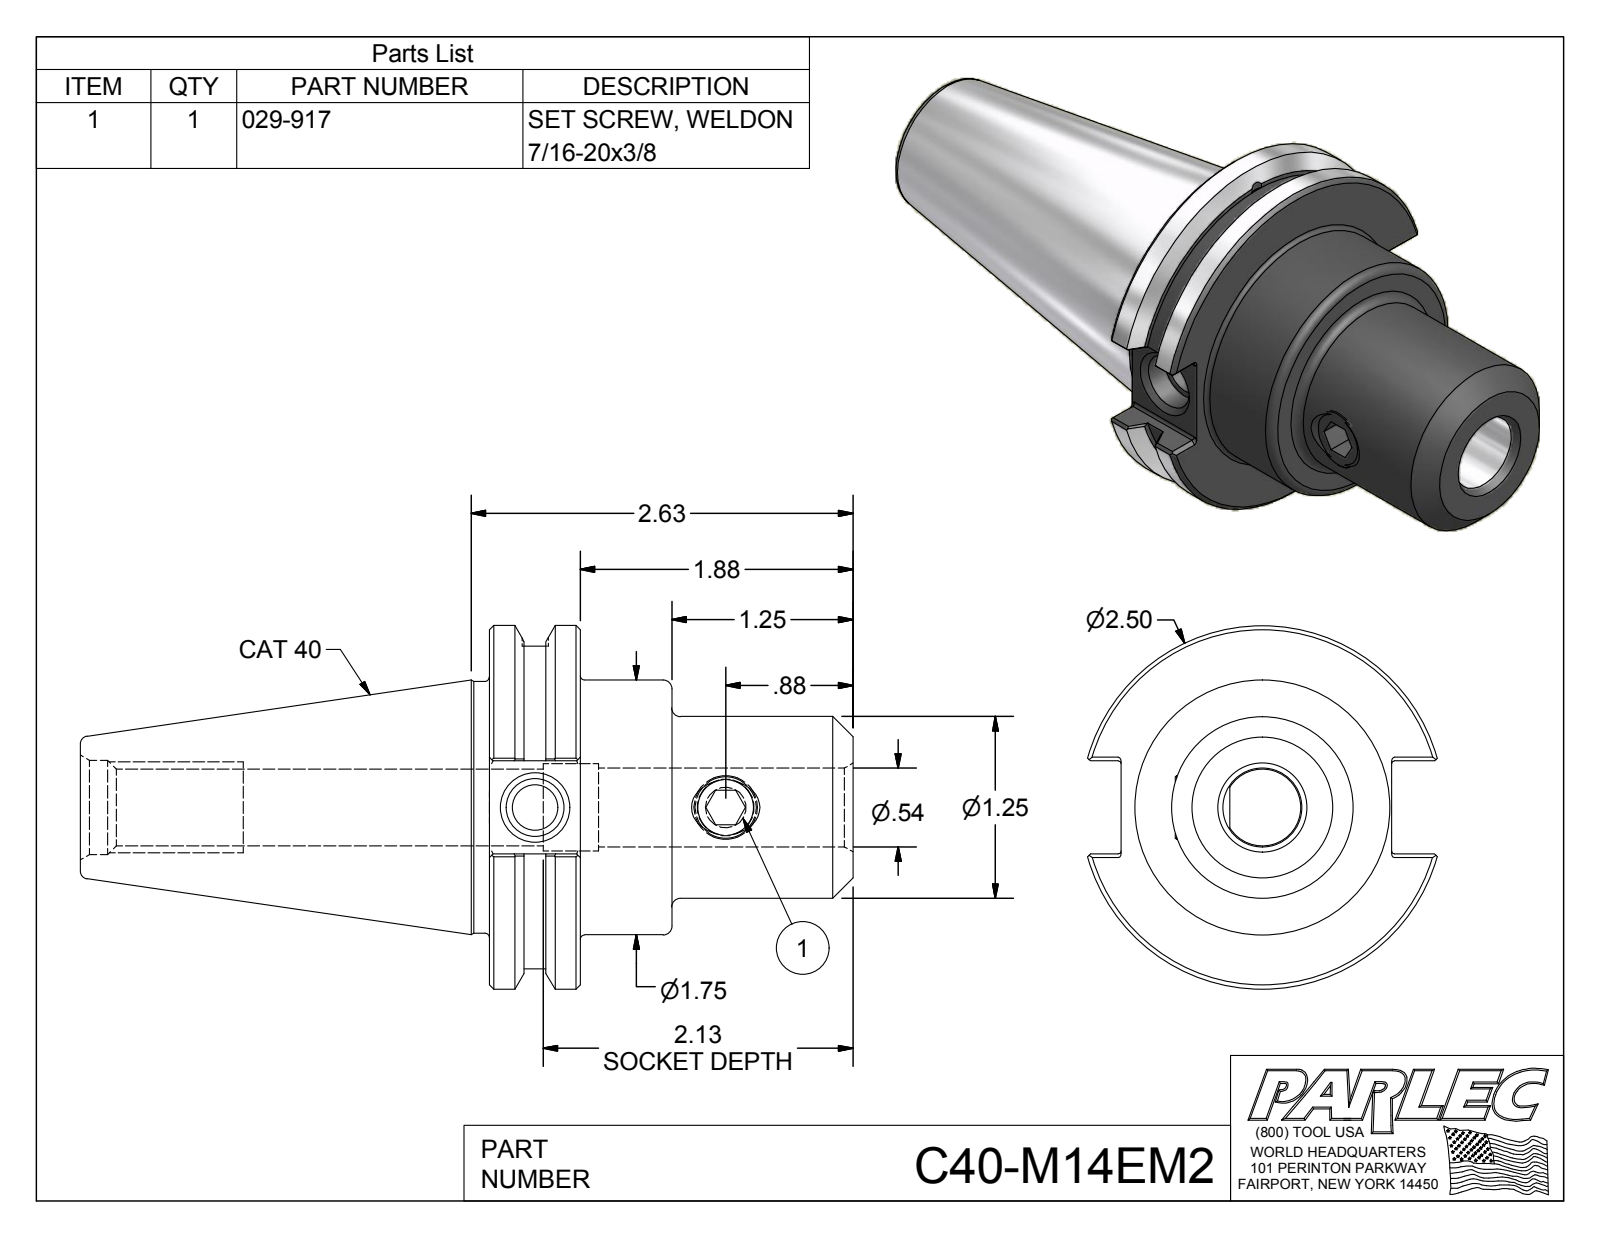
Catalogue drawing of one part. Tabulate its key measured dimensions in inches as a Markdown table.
| quantity | value |
| --- | --- |
| part name | C40-M14EM2; C40-M14EM2-1; 029-917 |
| STEP written by | Autodesk Inventor 2012 (AUTOMOTIVE_DESIGN) |
| units | inches |
| bodies | 2 solids, 111 faces (47 planar, 31 cylindrical, 33 other) |
| overall size | 5.749 × 2.5 × 2.406 |
| volume | 8.67 in³ |
| surface area | 43.51 in² |
| round holes (diameter × count) | 0.315 × 1, 0.383 × 1, 0.399 × 1, 0.527 × 1, 0.541 × 1, 0.6 × 1, 0.648 × 1 |
| round bosses / shafts (diameter × count) | 2.5 × 1, 2.219 × 1, 1.75 × 1, 1.73 × 1, 1.25 × 1, 0.437 × 1 |
| partial cylindrical surfaces (radius × count) | 0.02 × 12, 0.09 × 1 |
| main face-to-face distances | 0.625, 1.255, 0.63, 2.5, 1.875, 1.245, 0.236, 0.64, 1.86, 2.812 |
| hole center spacings | 1.31 |
